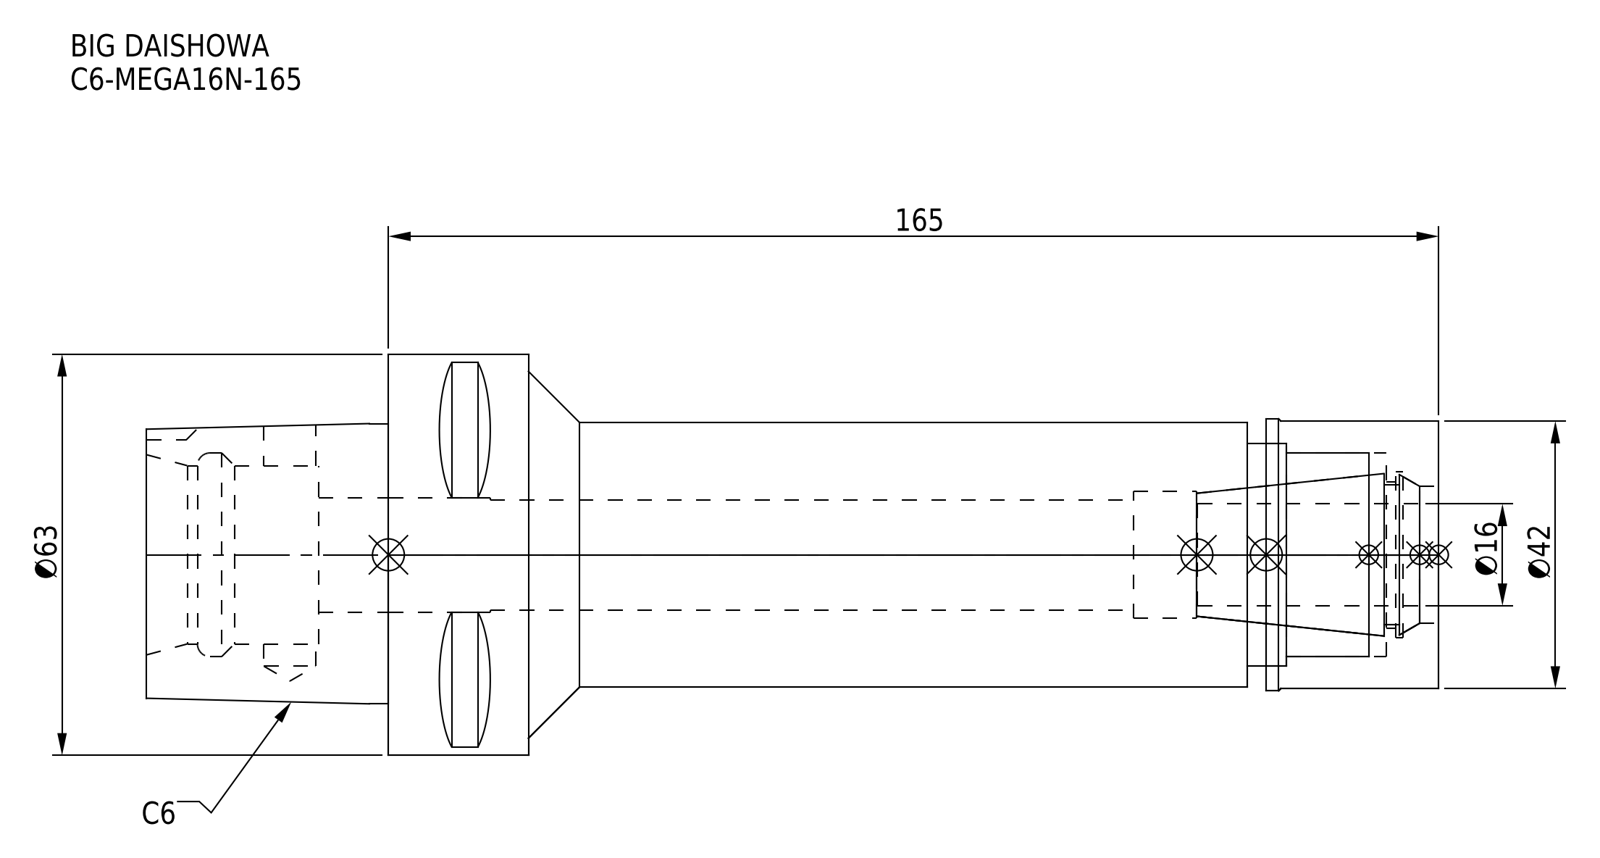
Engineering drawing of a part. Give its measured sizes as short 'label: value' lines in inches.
name: MGN16_1.stp; C6-MEGA16N-165; DXF_TEMP_ASSY_ASM_4_ASM.stp; C6-MEGA16N-165-160-FreeParts (+3 more)
written by: SolidWorks 2019 (CONFIG_CONTROL_DESIGN)
unit: in
bodies: 2 solids, 95 faces (38 planar, 39 cylindrical, 18 other)
size: 7.992 × 2.48 × 2.48
volume: 15.4 in³; area: 80.74 in²
holes: 1× ⌀0.319, 1× ⌀0.681, 1× ⌀0.709, 1× ⌀0.787, 1× ⌀0.846, 1× ⌀0.906, 1× ⌀1.024, 1× ⌀1.102, 1× ⌀1.26, 1× ⌀1.378
bosses: 1× ⌀2.48, 1× ⌀1.681, 1× ⌀1.654, 1× ⌀1.638
rounds: 1× R0.197
face distances: 6.496, 0.433, 1.496, 5.63, 0.866, 7.992, 2.362, 1.067, 4.563, 5.429
